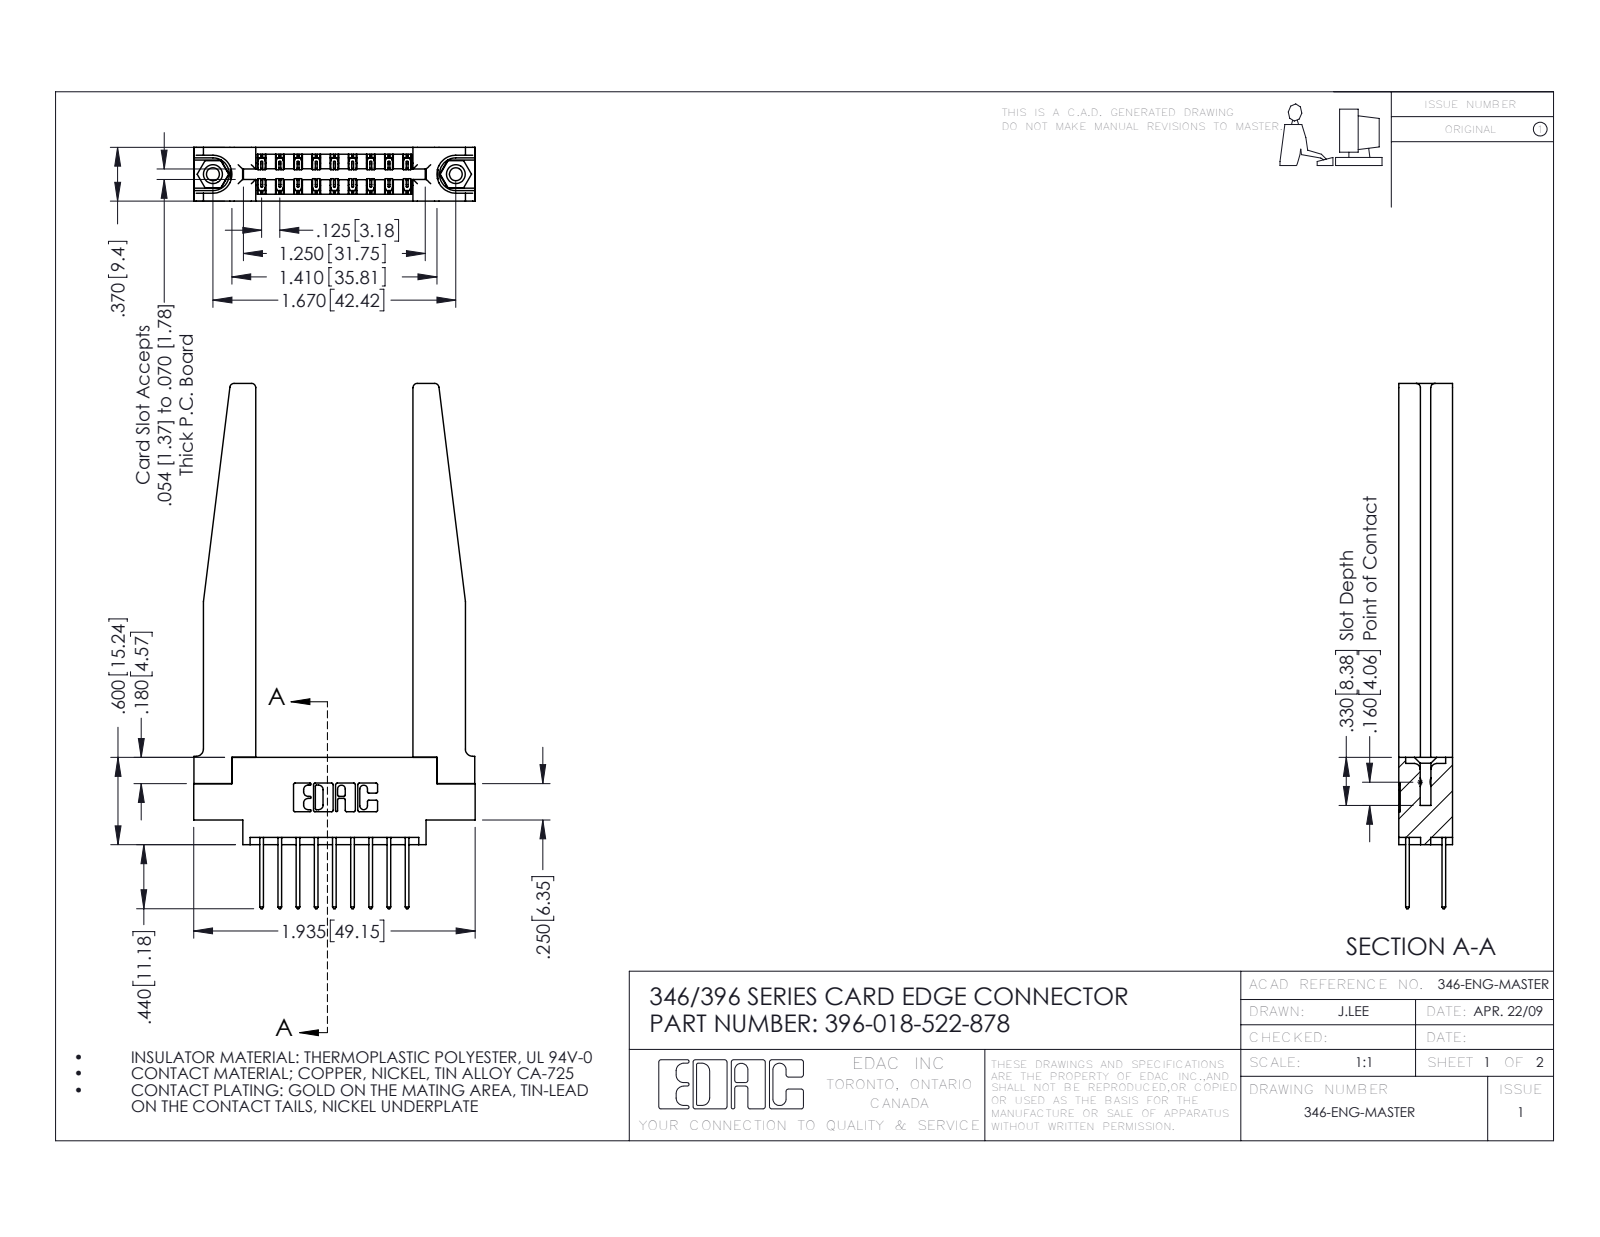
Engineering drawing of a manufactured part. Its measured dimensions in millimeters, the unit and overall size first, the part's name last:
Units: millimetres
Overall size (bounding box): 91.7 × 49.1 × 9.4
Round holes (diameter × count): ⌀2.3 ×2, ⌀3.2 ×2, ⌀4 ×2, ⌀1.6 ×1
Round bosses / shafts (diameter × count): ⌀3.9 ×2
Partial cylindrical surfaces — rounded edges, fillets, slot ends (radius × count): R0.2 ×27, R0.3 ×22, R0.3 ×18, R0.8 ×8, R0.2 ×6, R0.8 ×6, R0.7 ×3, R0.4 ×2
Main face-to-face distances: 9.4, 3.8, 1.8, 3.8, 1.2, 8.2, 6.4, 2.6, 5.6, 4.4
Hole centre spacings: 6.2, 37.2, 42.4
Volume: 11 300 mm³ · Surface area: 12 500 mm²
Bodies: 23 solids, 1296 faces (852 planar, 392 cylindrical, 52 other)
Part name (STEP PRODUCT): 345-292-001_345-293-122; 396-018-522-878; 346-220-078_345-220-078; 346 Part_0.170 Offset - 0.156 Dia-TH (+1 more)
STEP written by: SolidWorks 2016 (CONFIG_CONTROL_DESIGN)
